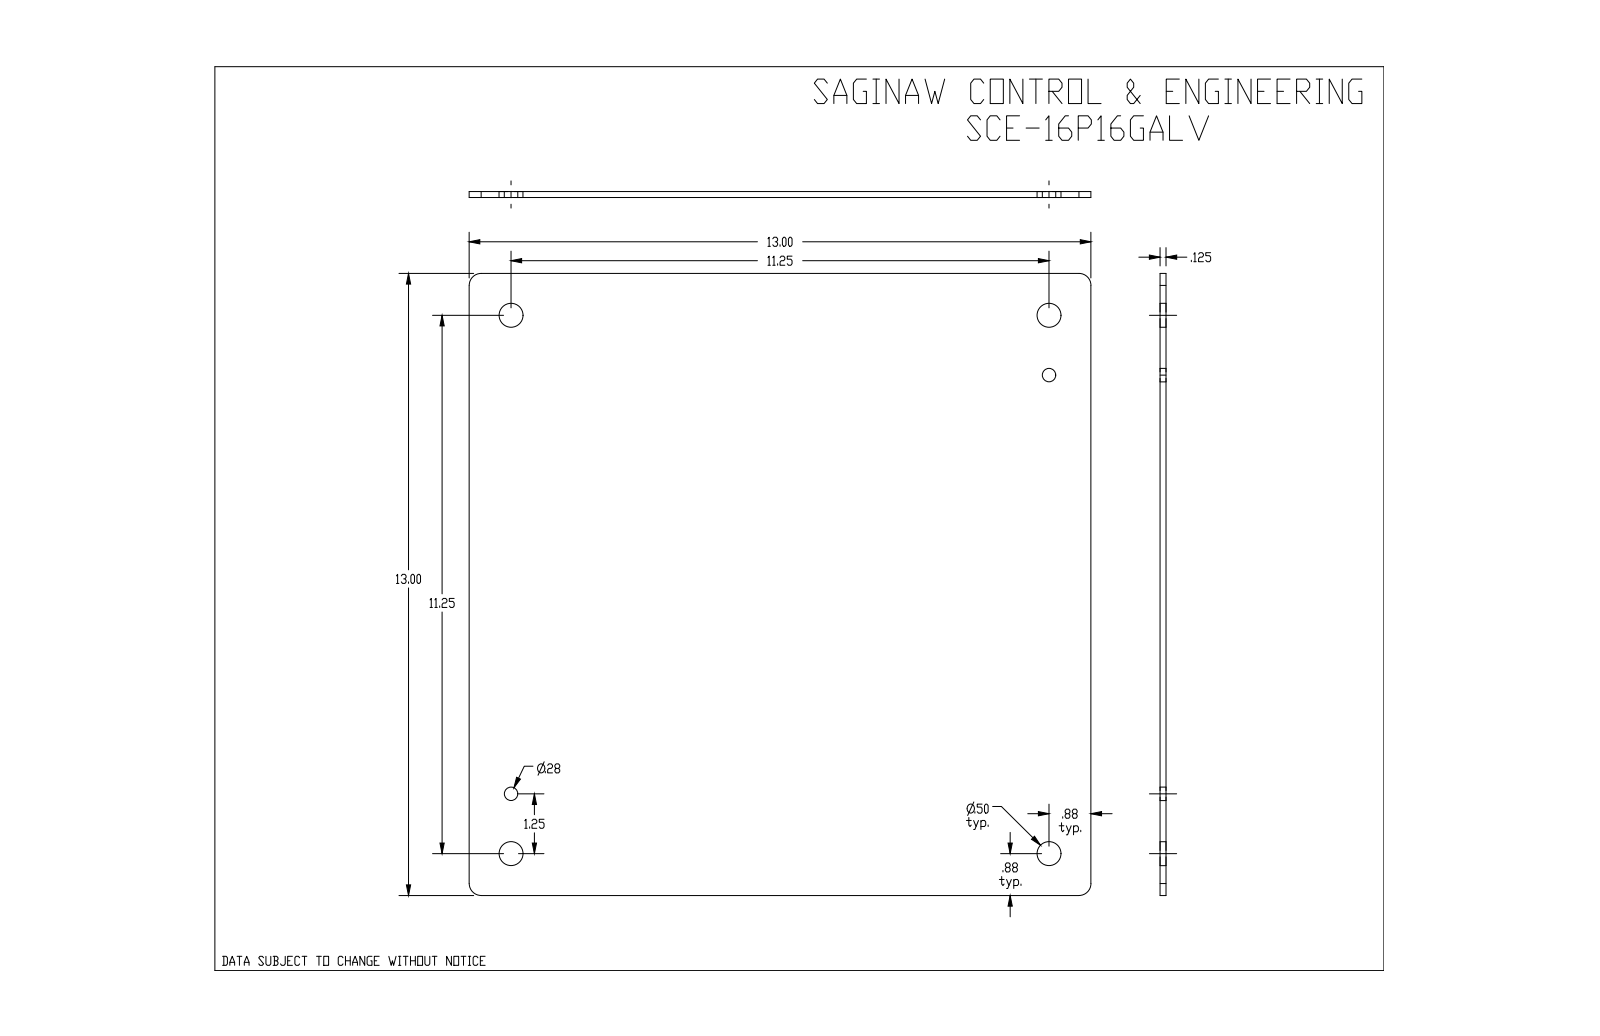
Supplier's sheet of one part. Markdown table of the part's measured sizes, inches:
| quantity | value |
| --- | --- |
| part name | SCE-16P16GALV |
| STEP written by | SolidWorks 2019 (CONFIG_CONTROL_DESIGN) |
| units | inches |
| bodies | 1 solid, 16 faces (6 planar, 10 cylindrical, 0 other) |
| overall size | 13 × 13 × 0.125 |
| volume | 21 in³ |
| surface area | 343.5 in² |
| round holes (diameter × count) | 0.5 × 4, 0.281 × 1, 0.281 × 1 |
| partial cylindrical surfaces (radius × count) | 0.25 × 4 |
| main face-to-face distances | 0.125, 13 |
| hole center spacings | 11.25, 1.25, 10, 11.32, 15.052, 15.911, 14.252 |
